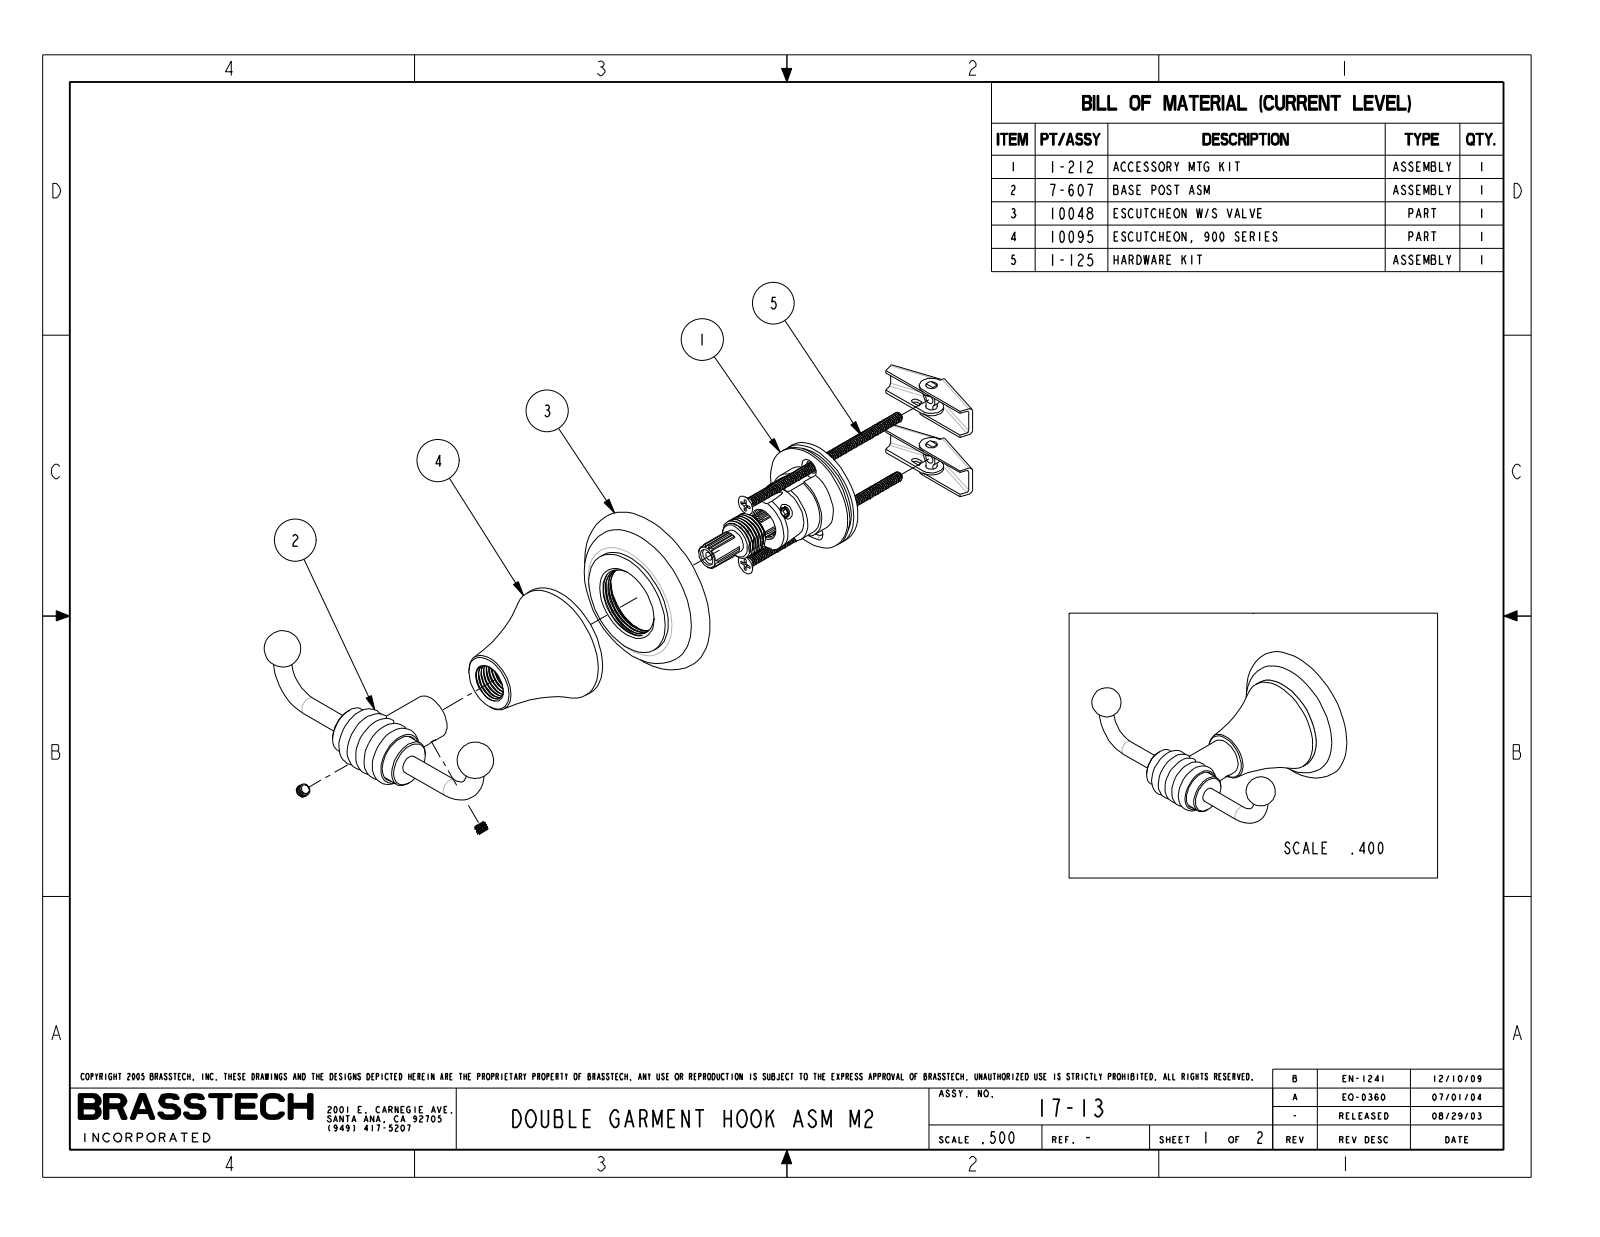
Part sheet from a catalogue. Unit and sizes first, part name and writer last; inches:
Units: inches
Overall size (bounding box): 4.25 × 3.2 × 2.36
Round holes (diameter × count): ⌀0.65 ×1
Round bosses / shafts (diameter × count): ⌀1.625 ×1, ⌀0.656 ×1, ⌀0.625 ×1, ⌀0.25 ×1
Partial cylindrical surfaces — rounded edges, fillets, slot ends (radius × count): R0.34 ×1
Main face-to-face distances: 0.375, 0.188, 1, 1.775, 1.4, 0.812, 1.188
Bodies: 0 solids, 53 faces (10 planar, 15 cylindrical, 28 other)
Part name (STEP PRODUCT): 17-13_WEB
STEP written by: PRO/ENGINEER BY PARAMETRIC TECHNOLOGY CORPORATION, 2009300 (CONFIG_CONTROL_DESIGN)
